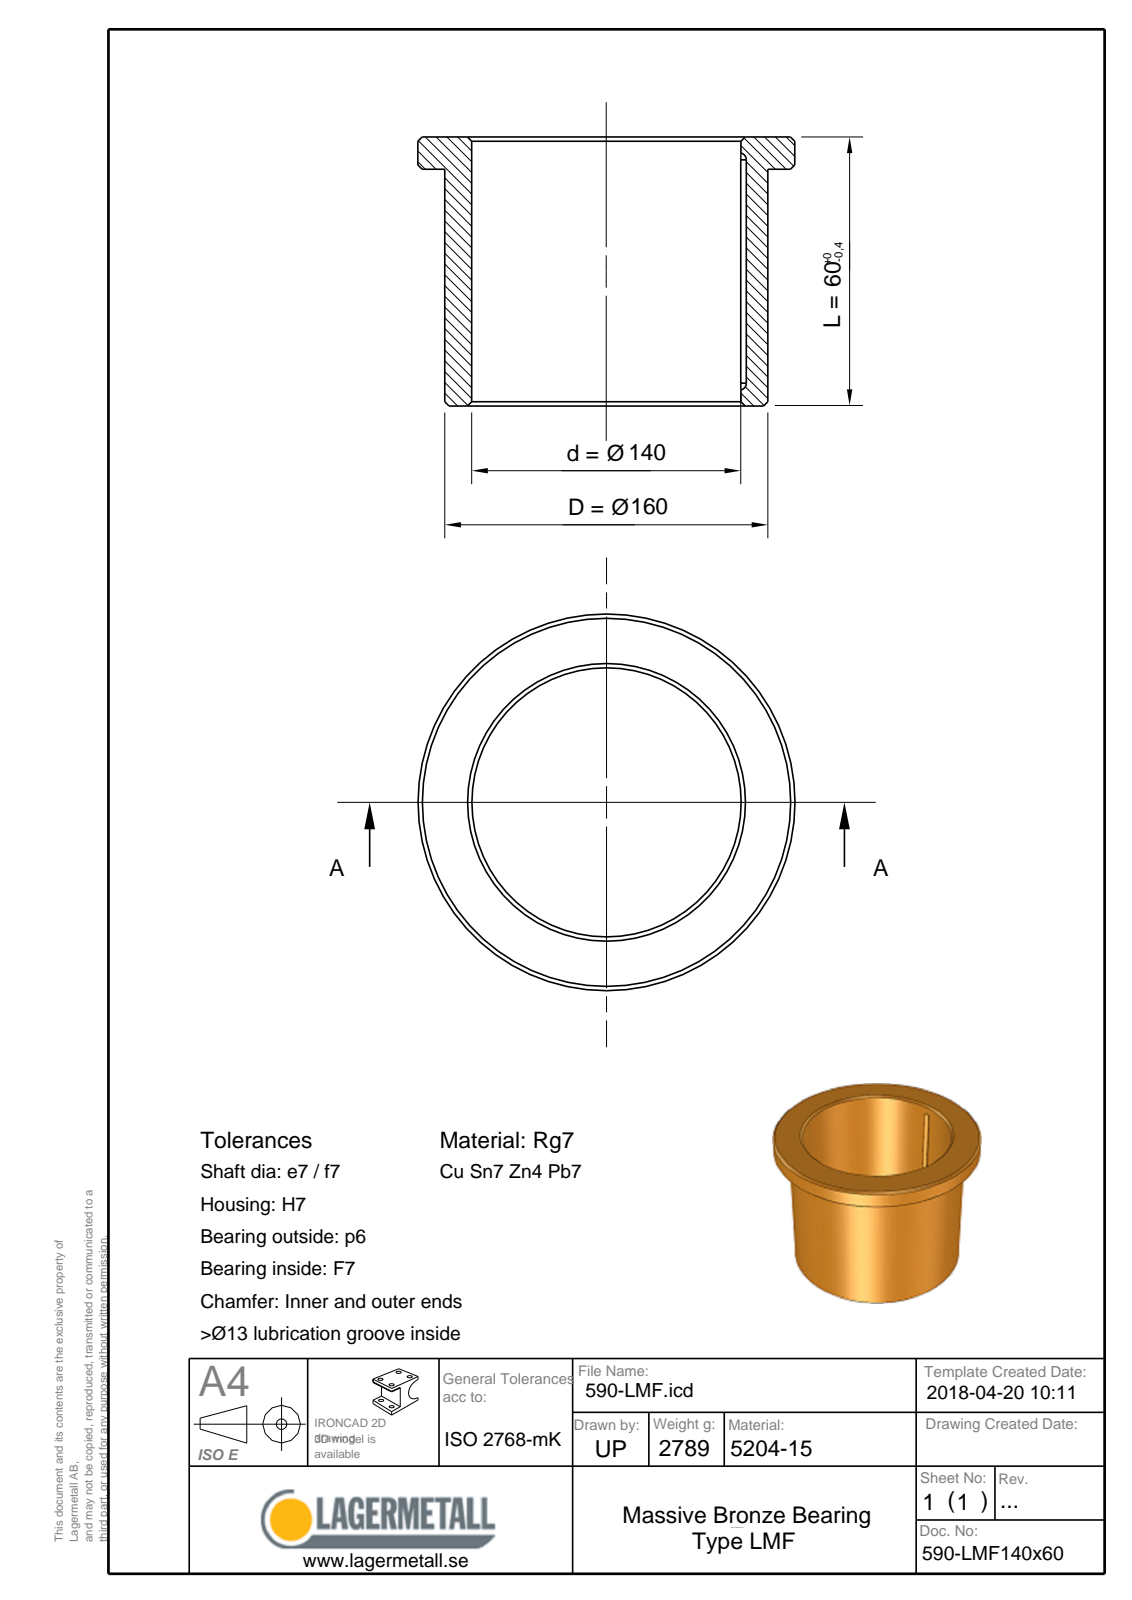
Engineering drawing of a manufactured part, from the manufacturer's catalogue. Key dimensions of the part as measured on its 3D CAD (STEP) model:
Part name (STEP PRODUCT): 590-LMF140x60
STEP written by: Spatial InterOp 3D (CONFIG_CONTROL_DESIGN)
Units: millimetres
Bodies: 1 solid, 16 faces (4 planar, 5 cylindrical, 7 other)
Overall size (bounding box): 175 × 175 × 60
Volume: 316 919 mm³ · Surface area: 71 536 mm²
Round holes (diameter × count): ⌀140 ×1
Round bosses / shafts (diameter × count): ⌀175 ×1, ⌀160 ×1
Partial cylindrical surfaces — rounded edges, fillets, slot ends (radius × count): R2.25 ×2
Main face-to-face distances: 10, 50, 60
